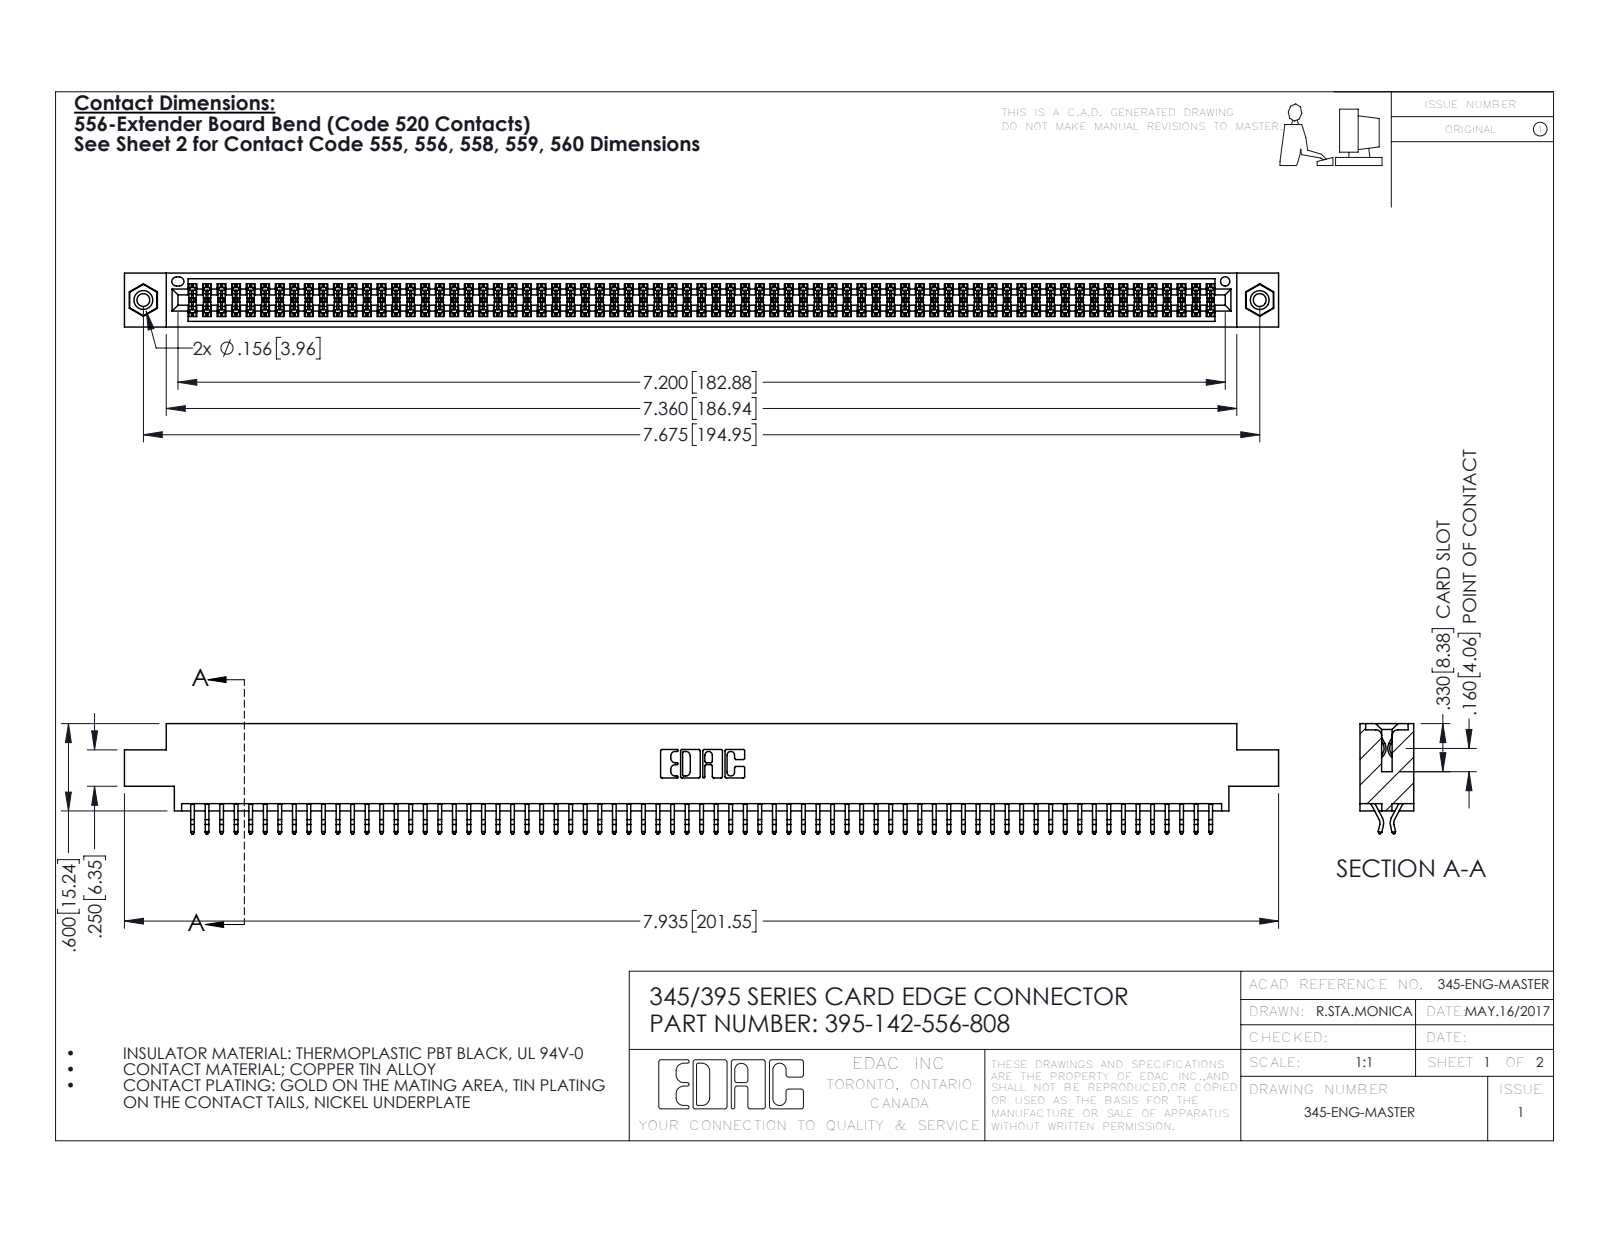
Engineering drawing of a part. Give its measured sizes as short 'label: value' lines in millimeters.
name: 345 Part_0.170 Offset - 0.156 Dia-TI; 345-292-001_556 Tail; 395-142-556-808; 345-250-001_345-250-003-102
written by: SolidWorks 2016 (CONFIG_CONTROL_DESIGN)
unit: mm
bodies: 145 solids, 8142 faces (5370 planar, 2756 cylindrical, 16 other)
size: 201.5 × 19.2 × 9.4
volume: 19 730 mm³; area: 29 750 mm²
holes: 2× ⌀2.3, 2× ⌀3.2, 2× ⌀4, 1× ⌀1.6
bosses: 2× ⌀3.9
rounds: 213× R0.2, 22× R0.3, 6× R0.2, 6× R0.8, 3× R0.7, 2× R0.3, 2× R0.4, 2× R0.5
face distances: 1.8, 7.6, 9.4, 5.1, 0.6, 2.5, 6.9, 5.7, 4.4, 3.8
hole spacings: 6.9, 189, 194.9
